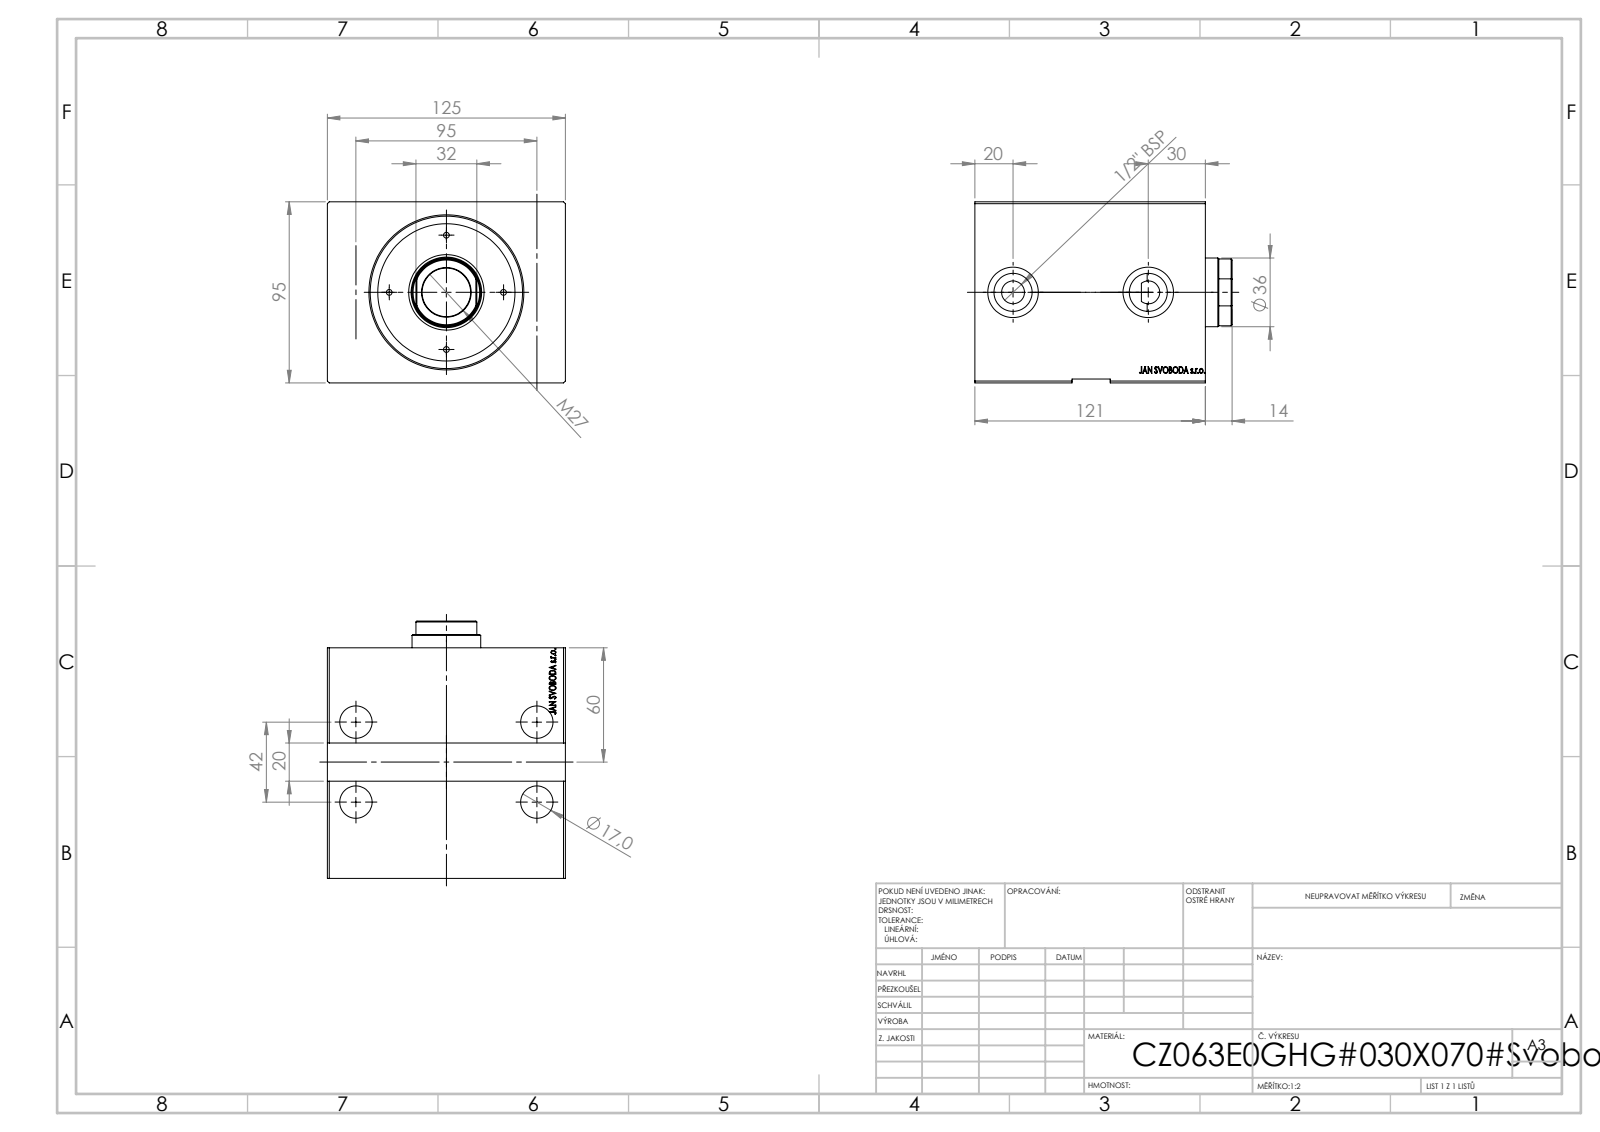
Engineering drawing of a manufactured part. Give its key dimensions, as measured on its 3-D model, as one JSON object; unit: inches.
{"step_written_by": "SolidWorks 2019 (CONFIG_CONTROL_DESIGN)", "units": "inches", "bodies": {"solids": 1, "faces": 805, "planar": 393, "cylindrical": 30, "other": 382}, "overall_size": [4.921, 4.764, 3.74], "volume_in3": 60.82, "surface_area_in2": 182.7, "round_holes": [[0.669, 4], [0.315, 2], [0.787, 2], [1.043, 2], [0.472, 1], [1.417, 1], [2.48, 1], [3.15, 1]], "partial_cylinders_radius": [[0.236, 1]], "face_to_face_distances": [3.74, 4.921, 4.764, 3.945, 0.819, 0.079, 3.661, 0.551, 3.394, 4.213], "hole_center_spacings": [1.654, 3.74, 4.089, 1.064, 1.133, 1.933, 2.008, 2.307]}
